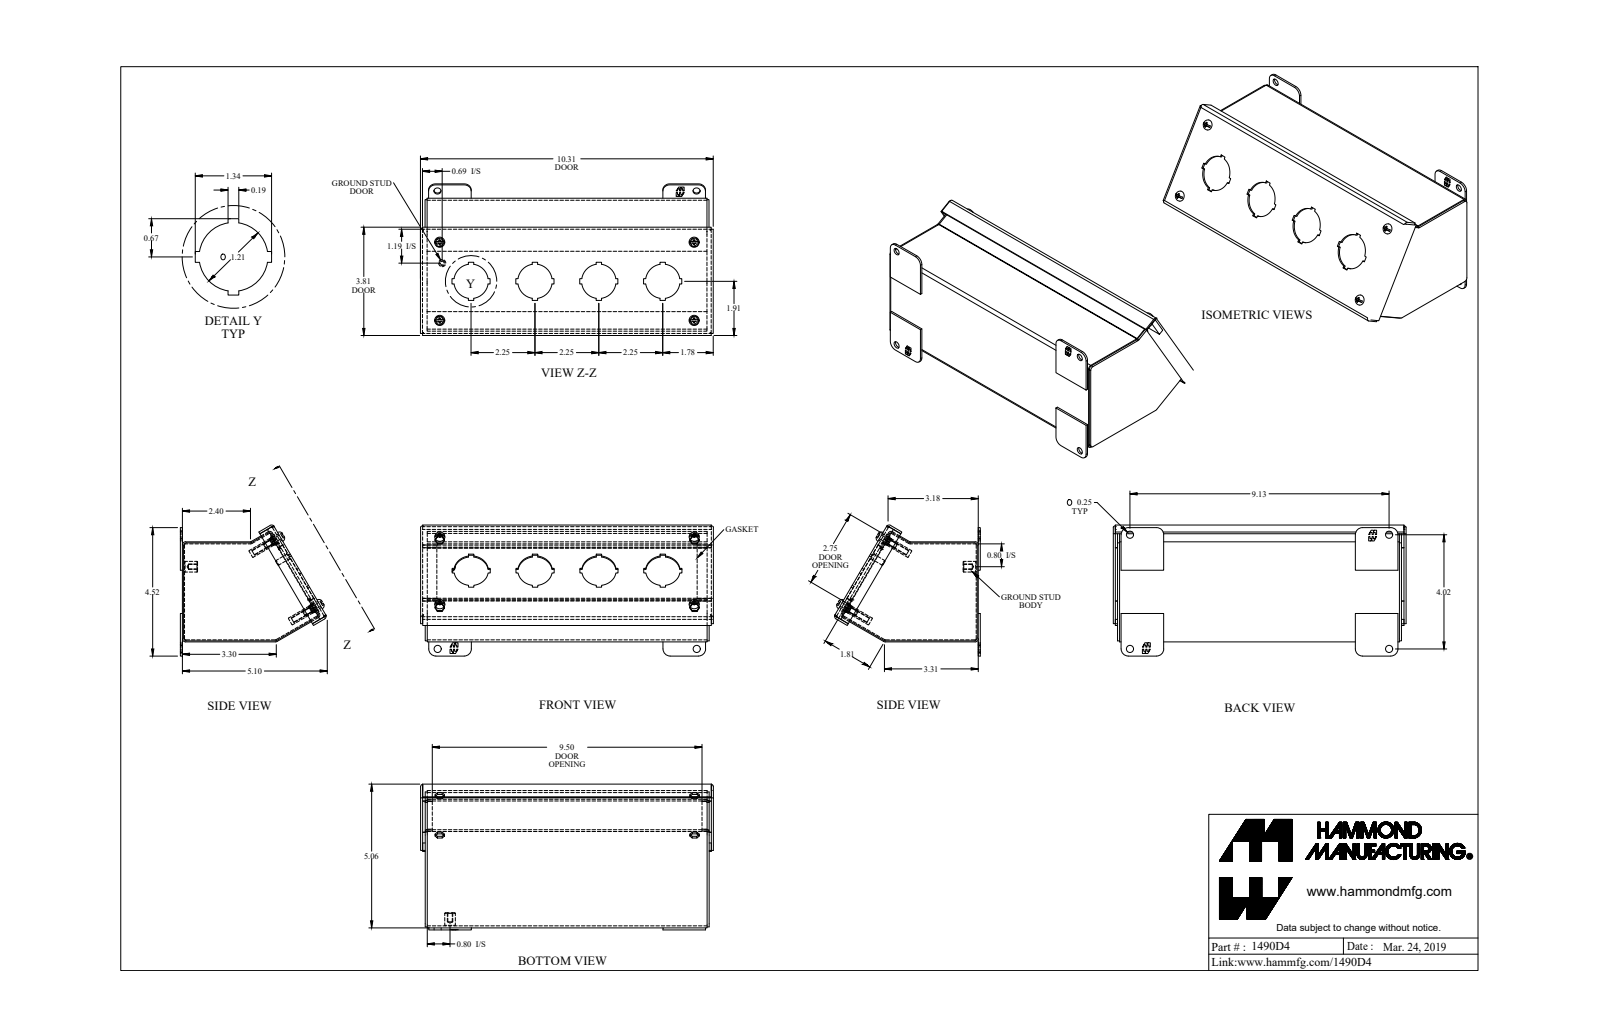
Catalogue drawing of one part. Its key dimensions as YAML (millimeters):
part_name: "1490D4_Default"
step_written_by: "SolidWorks 2019 (CONFIG_CONTROL_DESIGN)"
units: millimeters
bodies: {solids: 26, faces: 697, planar: 493, cylindrical: 164, other: 40}
overall_size: [261.9, 130.4, 117.2]
volume: 307300
surface_area: 315700
round_holes:
  - {diameter: 6.4, count: 8}
  - {diameter: 4, count: 4}
  - {diameter: 30.7, count: 4}
  - {diameter: 4, count: 1}
round_bosses_or_shafts:
  - {diameter: 9.9, count: 4}
  - {diameter: 7, count: 4}
  - {diameter: 4.8, count: 4}
  - {diameter: 3.8, count: 4}
  - {diameter: 9.5, count: 1}
  - {diameter: 6.4, count: 1}
  - {diameter: 4.8, count: 1}
partial_cylinders:
  - {radius: 2.7, count: 18}
  - {radius: 0.9, count: 12}
  - {radius: 6.4, count: 8}
  - {radius: 3.2, count: 4}
  - {radius: 4.1, count: 4}
  - {radius: 4.3, count: 4}
face_to_face_distances: [1.8, 87.6, 252.2, 89.5, 85.8, 4.8, 250.3, 254, 87.1, 4.3]
hole_center_spacings: [44.8, 92.1, 146.6, 202.5, 227.6, 227.9, 57.2, 69.7]
